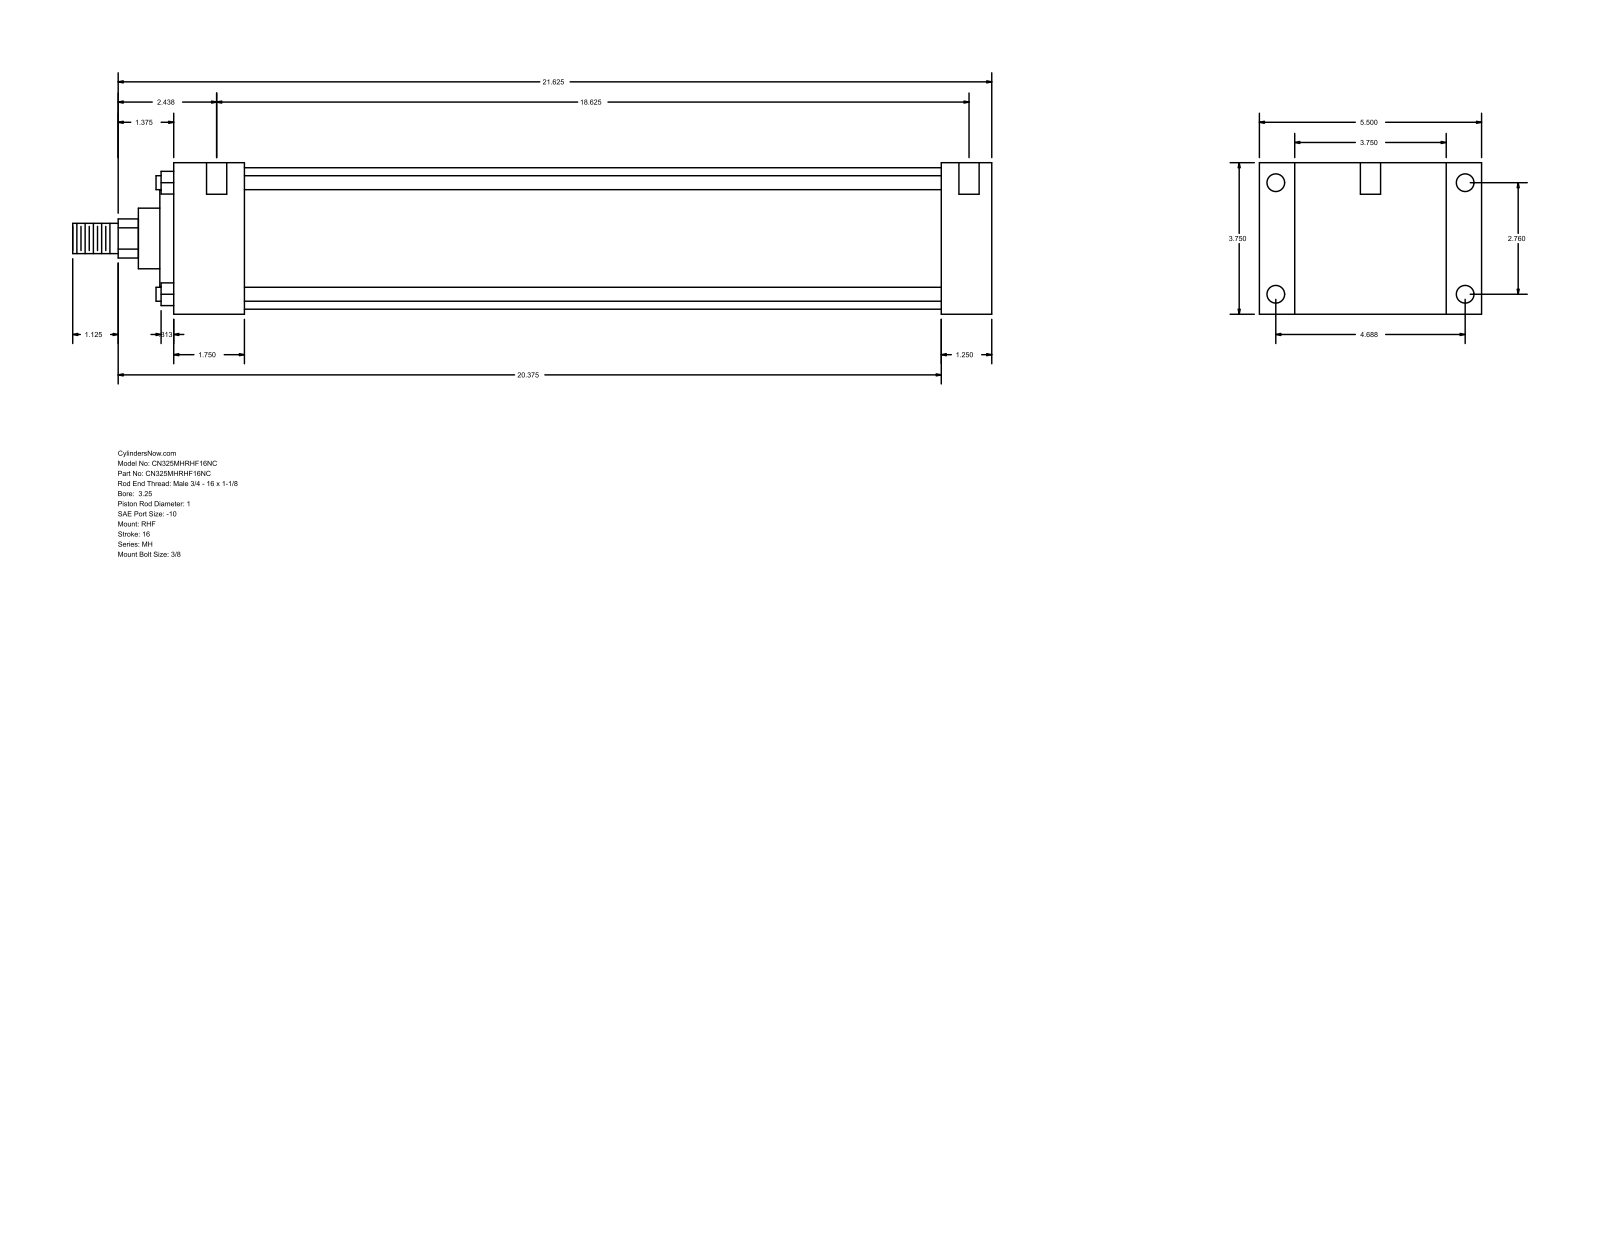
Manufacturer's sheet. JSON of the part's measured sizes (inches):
{"part_name": "MH_RHF__0325_1", "step_written_by": "GSSL Pune (CONFIG_CONTROL_DESIGN)", "units": "inches", "bodies": {"solids": 0, "faces": 90, "planar": 61, "cylindrical": 29, "other": 0}, "overall_size": [22.75, 5.5, 3.75], "round_holes": [[0.219, 4], [0.438, 4], [0.5, 2]], "round_bosses_or_shafts": [[0.345, 4], [3.5, 1], [2.375, 1], [1.5, 1], [1, 1], [0.75, 1]], "partial_cylinders_radius": [[0.484, 1]], "face_to_face_distances": [3.75, 1.25, 0.875, 4.625, 19, 20.25, 5.5, 1.75, 17.25, 18.5], "hole_center_spacings": [2.76, 4.687, 5.439, 18.875, 0.062, 0.187, 18.625, 18.687]}
